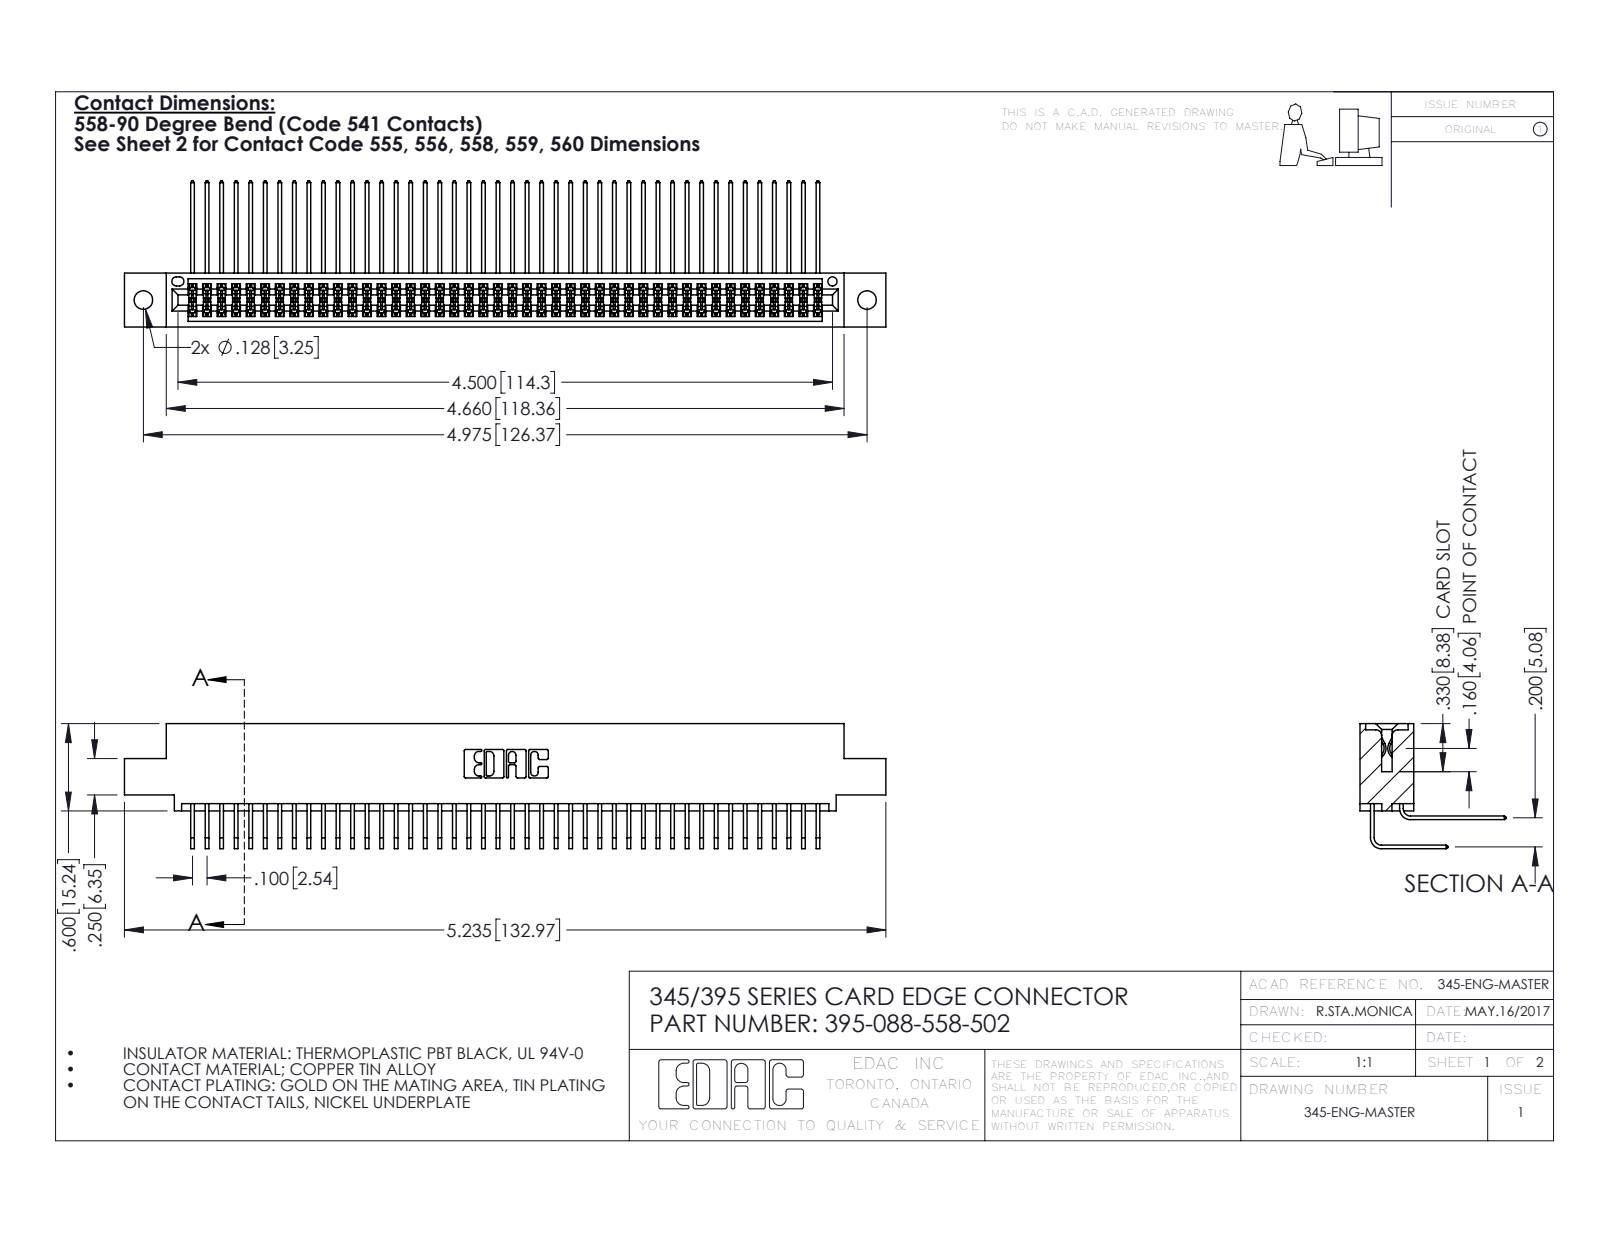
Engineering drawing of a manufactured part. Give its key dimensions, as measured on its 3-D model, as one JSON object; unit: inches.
{"part_name": "345 Part_0.110 Offset - 0.128 Dia; 395-088-558-502; 345-292-001_558 559 Tail - 1; 345-292-001_558 Tail - 2", "step_written_by": "SolidWorks 2016 (CONFIG_CONTROL_DESIGN)", "units": "inches", "bodies": {"solids": 89, "faces": 4706, "planar": 3164, "cylindrical": 1542, "other": 0}, "overall_size": [5.235, 1.005, 0.859], "volume_in3": 0.814, "surface_area_in2": 34.03, "round_holes": [[0.128, 2], [0.064, 1]], "partial_cylinders_radius": [[0.006, 133], [0.01, 22], [0.007, 6], [0.031, 6], [0.026, 3], [0.014, 2], [0.019, 2], [0.022, 2]], "face_to_face_distances": [0.072, 0.298, 0.2, 0.37, 0.098, 0.272, 0.025, 0.225, 0.025, 0.175], "hole_center_spacings": [0.27, 4.739, 4.975]}
